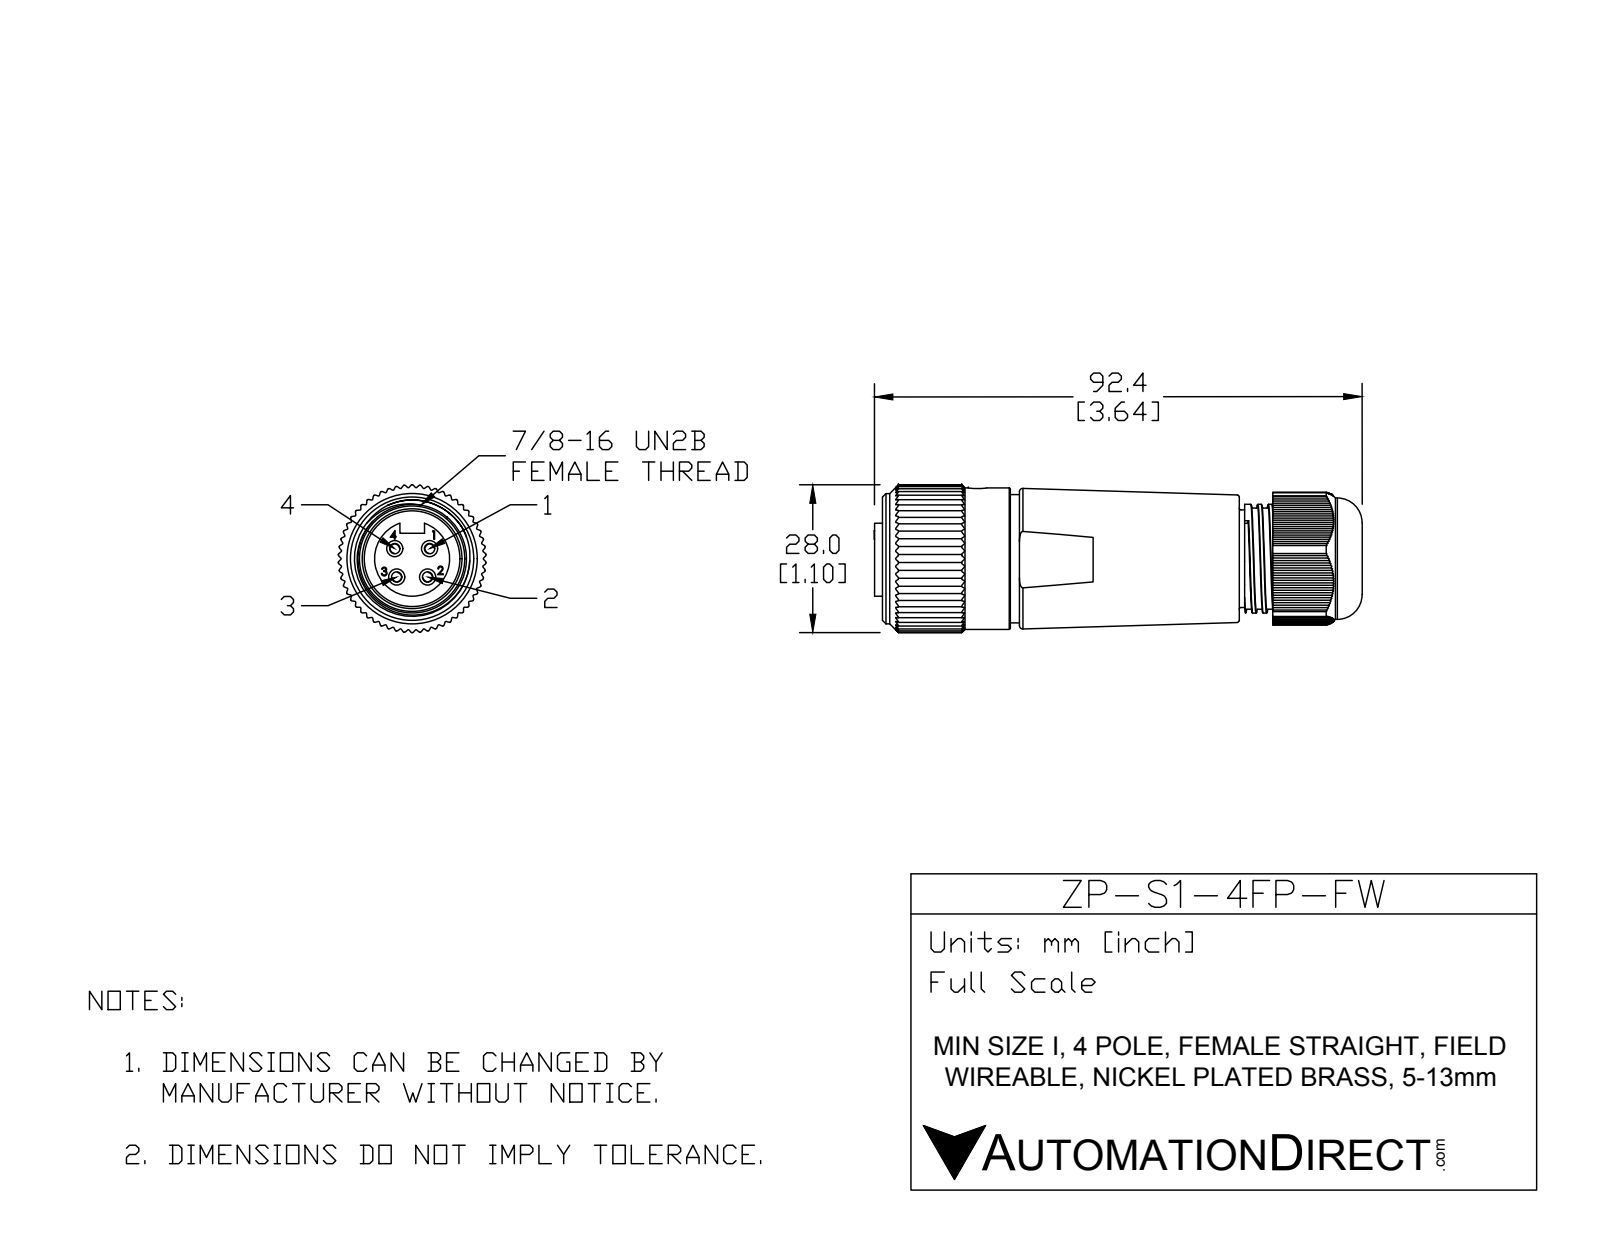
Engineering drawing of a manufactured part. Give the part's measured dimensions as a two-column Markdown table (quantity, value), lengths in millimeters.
| quantity | value |
| --- | --- |
| part name | MIN-4FP-FW |
| STEP written by | SolidWorks 2015 (AUTOMOTIVE_DESIGN) |
| units | millimeters |
| bodies | 1 solid, 833 faces (461 planar, 318 cylindrical, 54 other) |
| overall size | 92.46 × 28 × 27.96 |
| volume | 43 486 mm³ |
| surface area | 11 915 mm² |
| round holes (diameter × count) | 3.05 × 4, 3.5 × 1, 13.46 × 1, 20.57 × 1, 25.4 × 1 |
| round bosses / shafts (diameter × count) | 26.8 × 1, 24.68 × 1, 24.3 × 1, 24 × 1, 22.99 × 1, 20.6 × 1, 20 × 1, 18.14 × 1 |
| partial cylindrical surfaces (radius × count) | 0.25 × 116, 0.2 × 58, 13.23 × 1, 14 × 1 |
| main face-to-face distances | 0.36, 0.72, 1.08, 18.94, 6.35, 1.44, 69.11, 1.8, 15.39, 18.92 |
| hole center spacings | 3.81, 4.54, 5.39, 8.22, 5.84, 6.6 |
